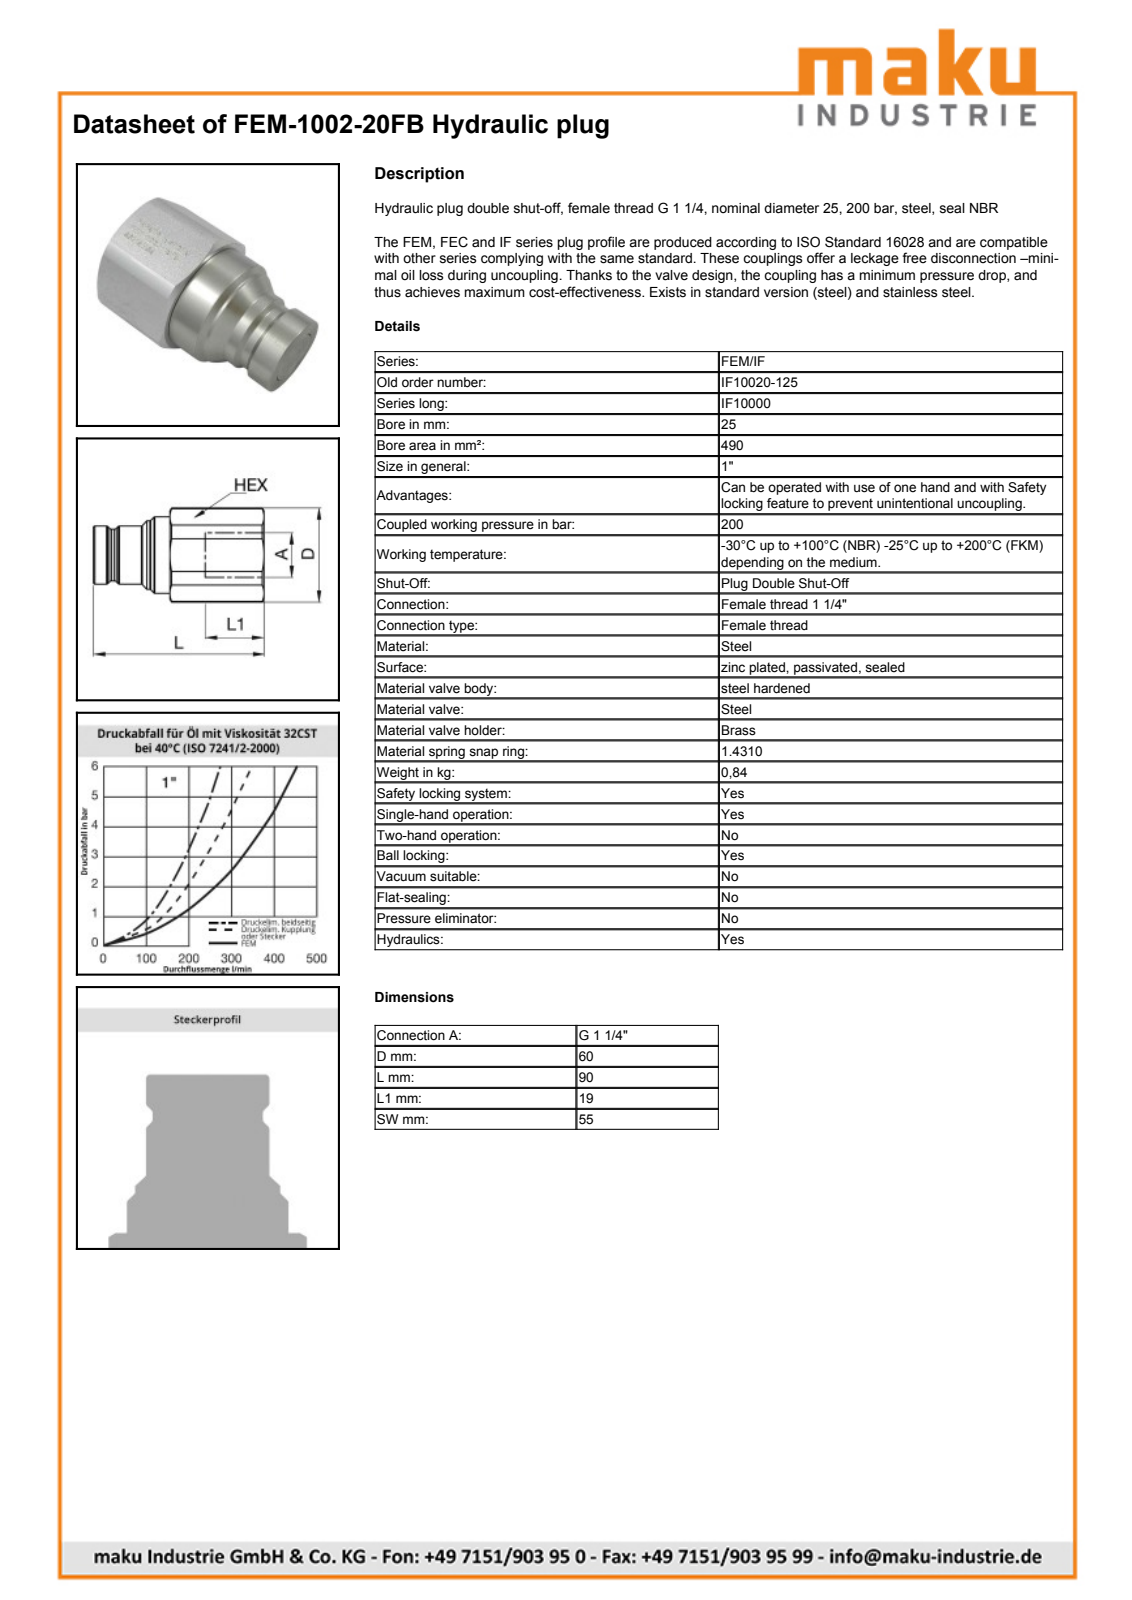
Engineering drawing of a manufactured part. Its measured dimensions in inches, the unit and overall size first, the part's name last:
Units: inches
Overall size (bounding box): 3.646 × 2.362 × 2.165
Round holes (diameter × count): ⌀0.933 ×1, ⌀1.533 ×1
Round bosses / shafts (diameter × count): ⌀1.969 ×1, ⌀1.783 ×1, ⌀1.417 ×1, ⌀1.26 ×1, ⌀0.924 ×1
Partial cylindrical surfaces — rounded edges, fillets, slot ends (radius × count): R1.181 ×1
Main face-to-face distances: 2.165, 3.646, 2.602, 1.044, 1.913, 0.688, 1.732, 1.909, 0.692, 1.736
Volume: 9.104 in³ · Surface area: 34.57 in²
Bodies: 1 solid, 83 faces (13 planar, 22 cylindrical, 48 other)
Part name (STEP PRODUCT): FEM-1002-20FB
STEP written by: SolidWorks 2009 (AUTOMOTIVE_DESIGN)
